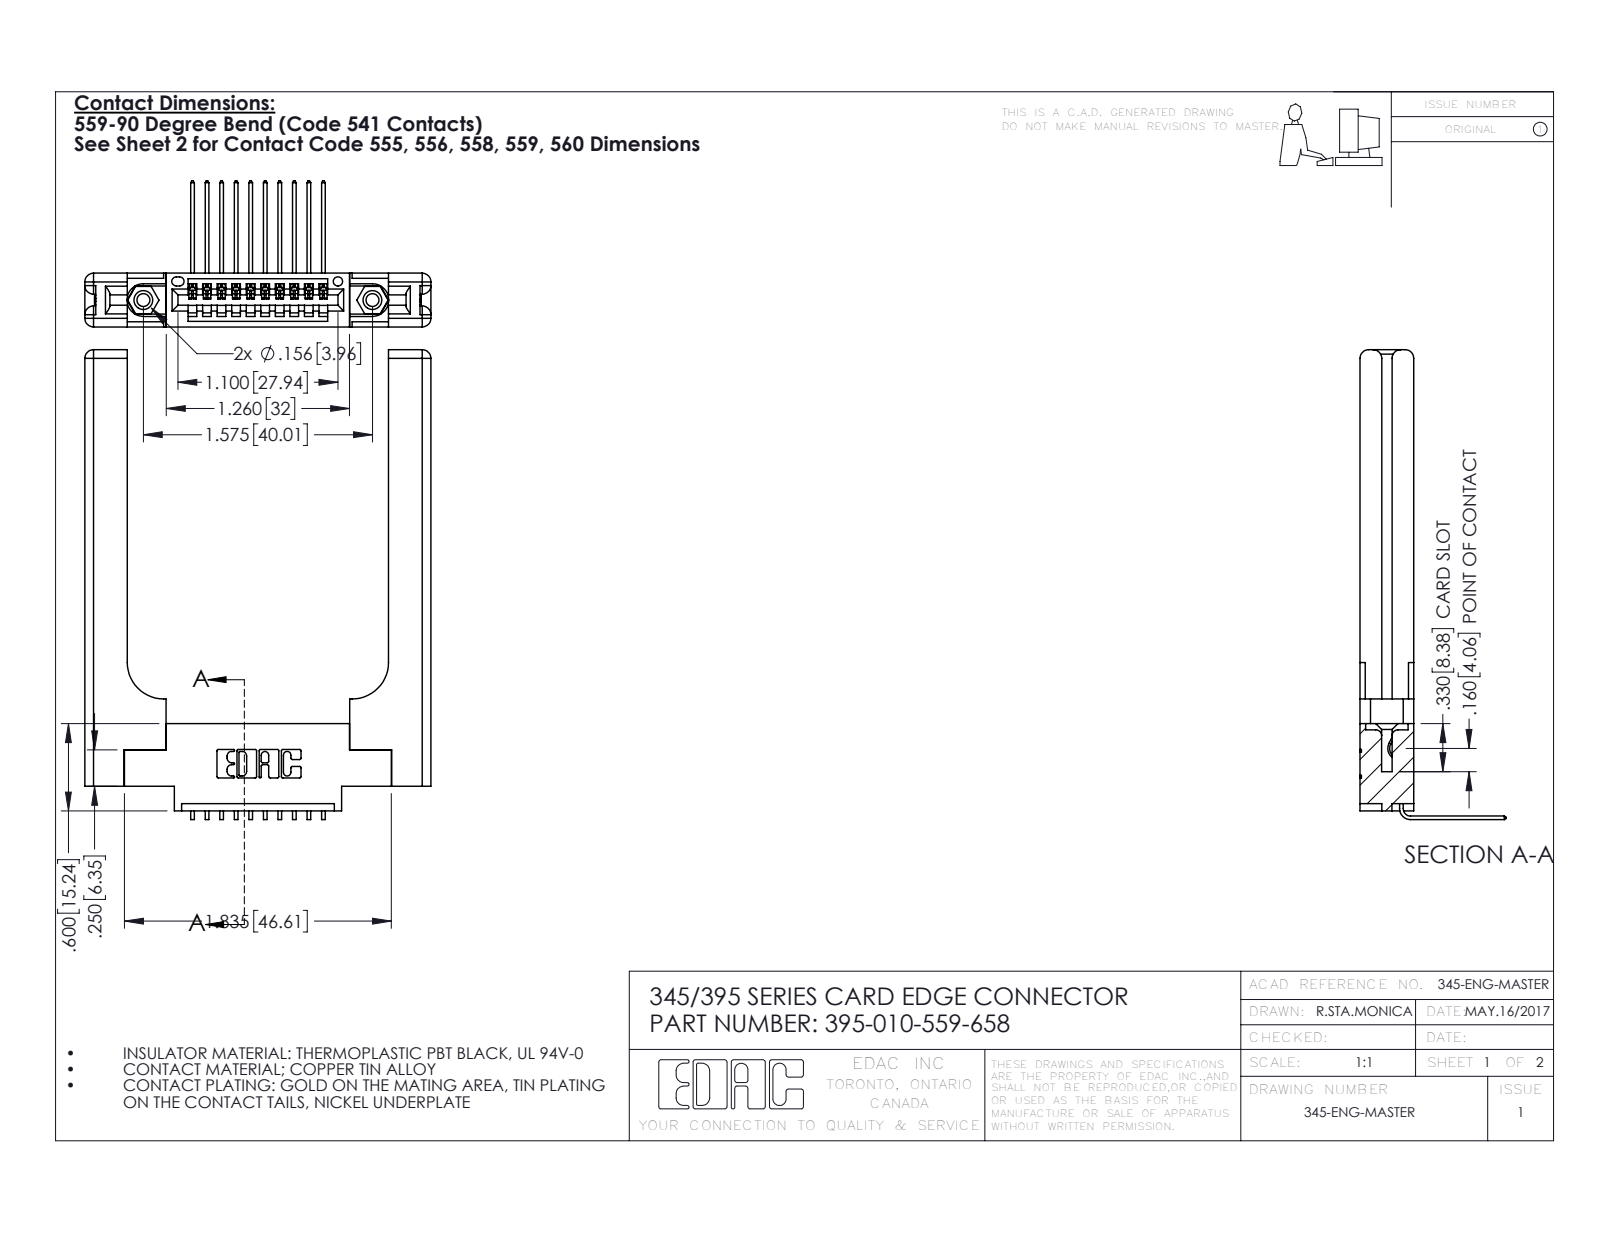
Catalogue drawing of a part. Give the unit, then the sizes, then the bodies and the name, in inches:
Units: inches
Overall size (bounding box): 3.229 × 2.379 × 1.005
Round holes (diameter × count): ⌀0.089 ×2, ⌀0.125 ×2, ⌀0.156 ×2, ⌀0.064 ×1
Round bosses / shafts (diameter × count): ⌀0.155 ×2
Partial cylindrical surfaces — rounded edges, fillets, slot ends (radius × count): R0.01 ×22, R0.006 ×20, R0.06 ×16, R0.007 ×6, R0.031 ×6, R0.026 ×3, R0.03 ×2, R0.031 ×2
Main face-to-face distances: 0.37, 0.15, 0.072, 0.22, 0.148, 0.077, 0.298, 1.796, 0.12, 0.071
Hole centre spacings: 0.27, 1.344, 1.575
Volume: 0.848 in³ · Surface area: 19.17 in²
Bodies: 15 solids, 986 faces (652 planar, 274 cylindrical, 60 other)
Part name (STEP PRODUCT): 345 Part_0.170 Offset - 0.156 Dia-TH; 345-220-058_345-220-058; 345-250-001_345-250-001-102; 395-010-559-658 (+1 more)
STEP written by: SolidWorks 2016 (CONFIG_CONTROL_DESIGN)
